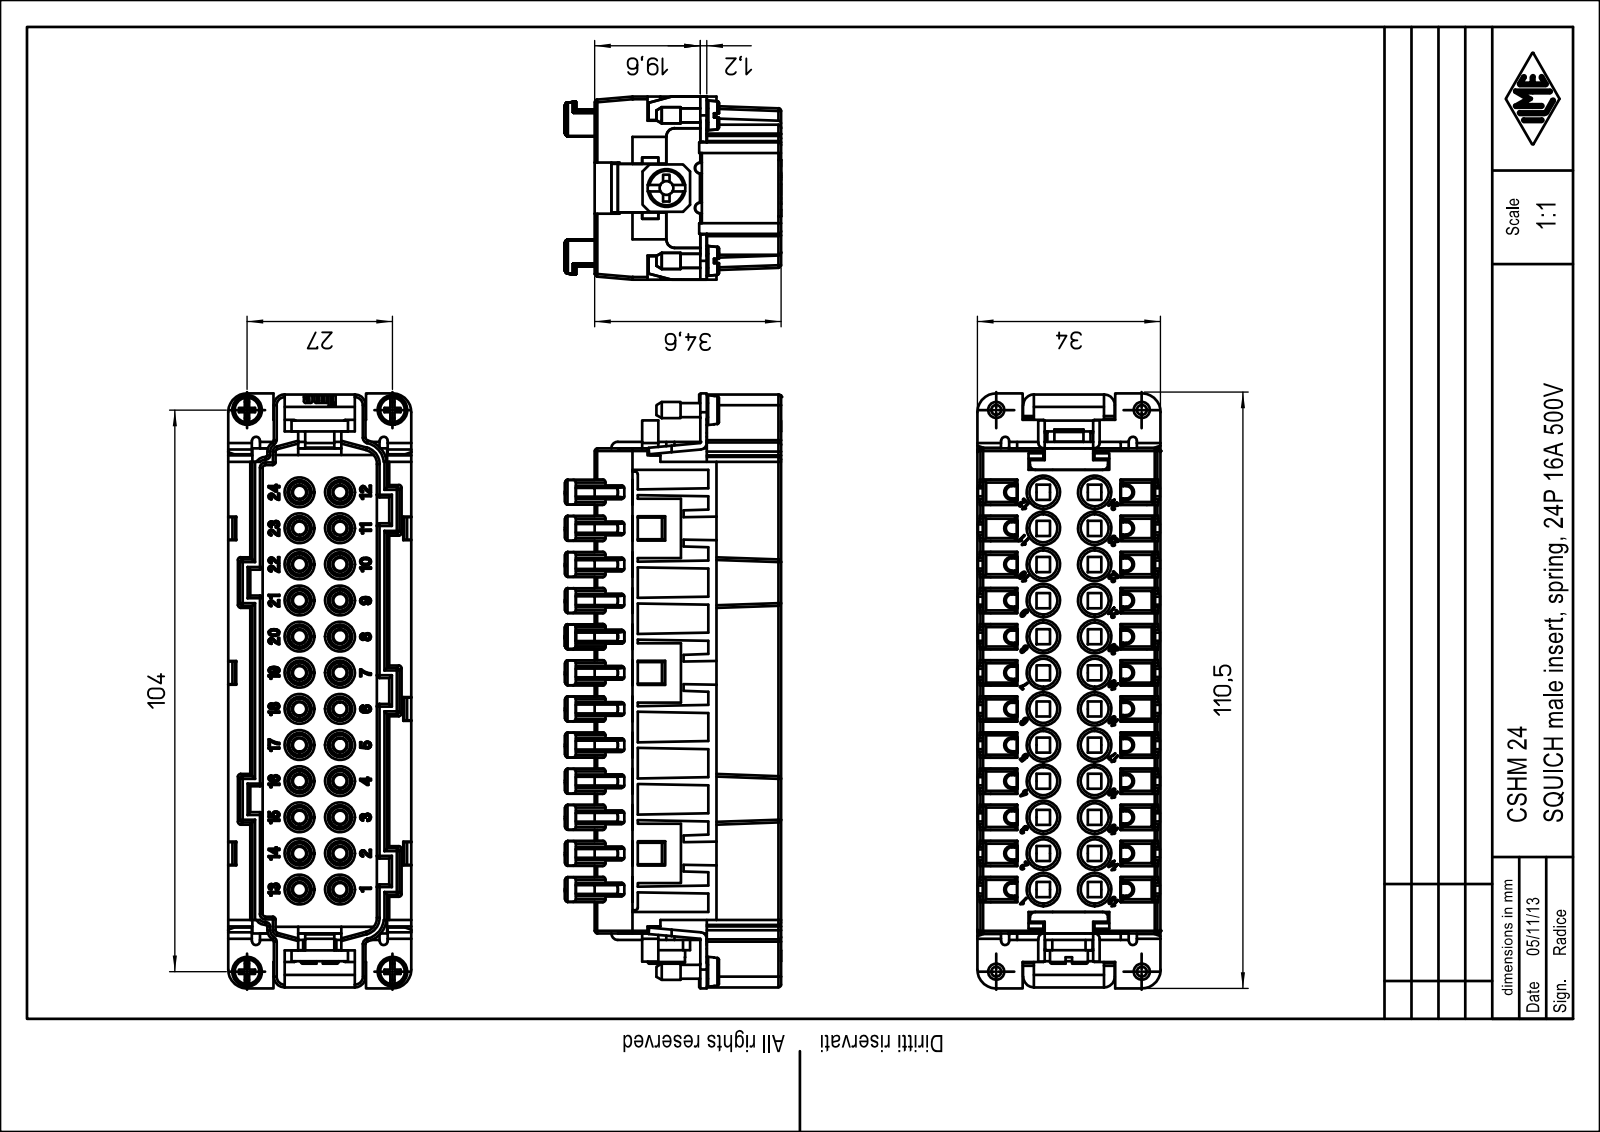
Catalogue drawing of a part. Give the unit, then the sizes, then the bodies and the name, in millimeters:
Units: millimetres
Overall size (bounding box): 110.4 × 40.1 × 34
Round holes (diameter × count): ⌀5 ×24, ⌀2.8 ×4, ⌀2.58 ×1, ⌀4.2 ×1
Round bosses / shafts (diameter × count): ⌀2.48 ×24, ⌀5.5 ×4, ⌀3 ×4, ⌀2.6 ×4, ⌀7 ×1, ⌀6 ×1, ⌀4 ×1
Partial cylindrical surfaces — rounded edges, fillets, slot ends (radius × count): R0.5 ×126, R0.2 ×50, R1.5 ×26, R1.27 ×24, R1 ×10, R2 ×10, R1.2 ×6, R0.75 ×4
Main face-to-face distances: 1.5, 26.1, 20.1, 4.9, 2.5, 6.4, 1, 1.2, 2, 27.6
Hole centre spacings: 6.7, 11.62, 13.4, 16.43, 20.1, 22.23, 26.8, 28.43
Volume: 71 395 mm³ · Surface area: 38 416 mm²
Bodies: 1 solid, 2421 faces (1621 planar, 480 cylindrical, 320 other)
Part name (STEP PRODUCT): CSHM_24
STEP written by: PTC Creo Elements/Direct Modeling 19.0E 27-Jun-2016 (C) Parametric Technology GmbH (AUTOMOTIVE_DESIGN)
